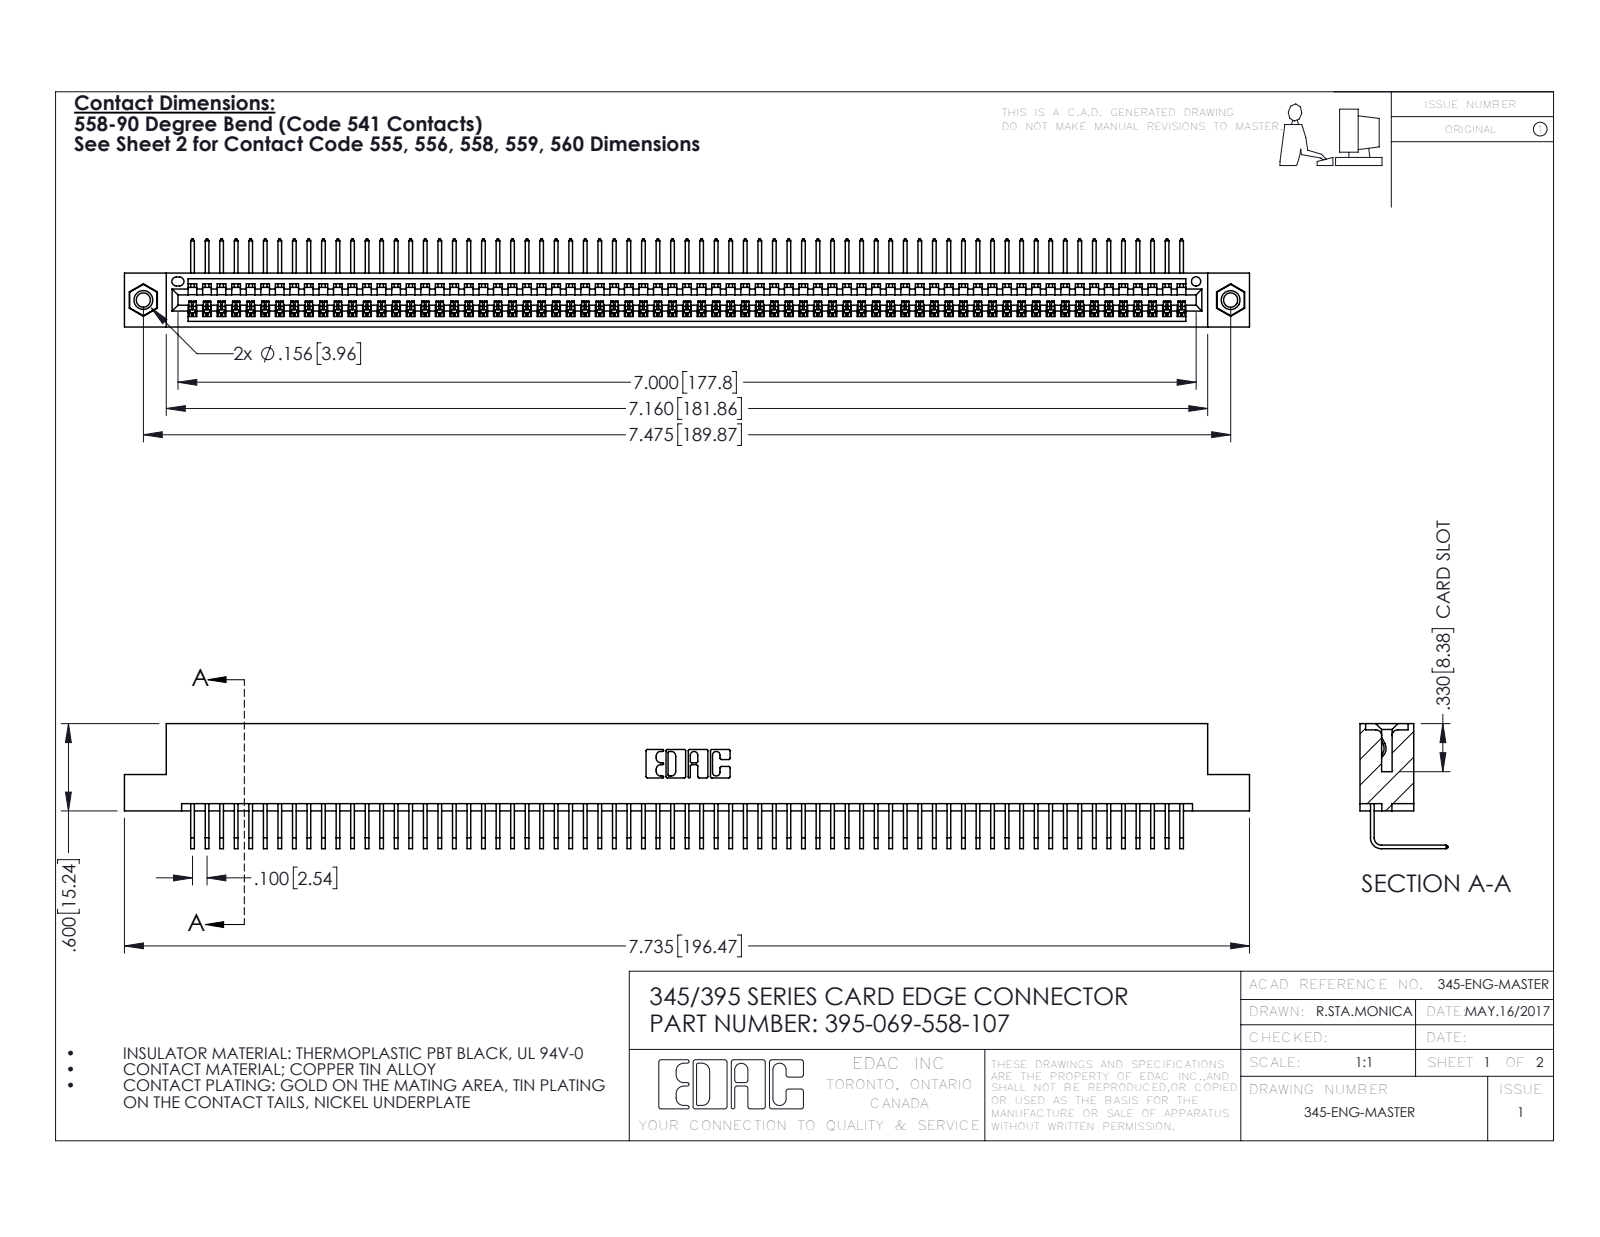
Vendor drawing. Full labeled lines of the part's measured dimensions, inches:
Part name (STEP PRODUCT): 345-292-001_558 Tail - 2; 345-250-001_345-250-005-103; 395-069-558-107; 345 Part_Flush Mounting Lugs - 0.156 Dia-TI
STEP written by: SolidWorks 2016 (CONFIG_CONTROL_DESIGN)
Units: inches
Bodies: 72 solids, 4326 faces (3010 planar, 1300 cylindrical, 16 other)
Overall size (bounding box): 7.735 × 0.859 × 0.605
Volume: 1.165 in³ · Surface area: 42.05 in²
Round holes (diameter × count): ⌀0.098 ×2, ⌀0.125 ×2, ⌀0.156 ×2, ⌀0.064 ×1
Round bosses / shafts (diameter × count): ⌀0.155 ×2
Partial cylindrical surfaces — rounded edges, fillets, slot ends (radius × count): R0.006 ×138, R0.01 ×22, R0.007 ×6, R0.031 ×6, R0.026 ×3, R0.031 ×2, R0.04 ×2, R0.014 ×1
Main face-to-face distances: 0.072, 0.298, 0.37, 0.2, 0.098, 0.272, 0.025, 0.225, 0.149, 0.072
Hole centre spacings: 0.27, 7.239, 7.475
